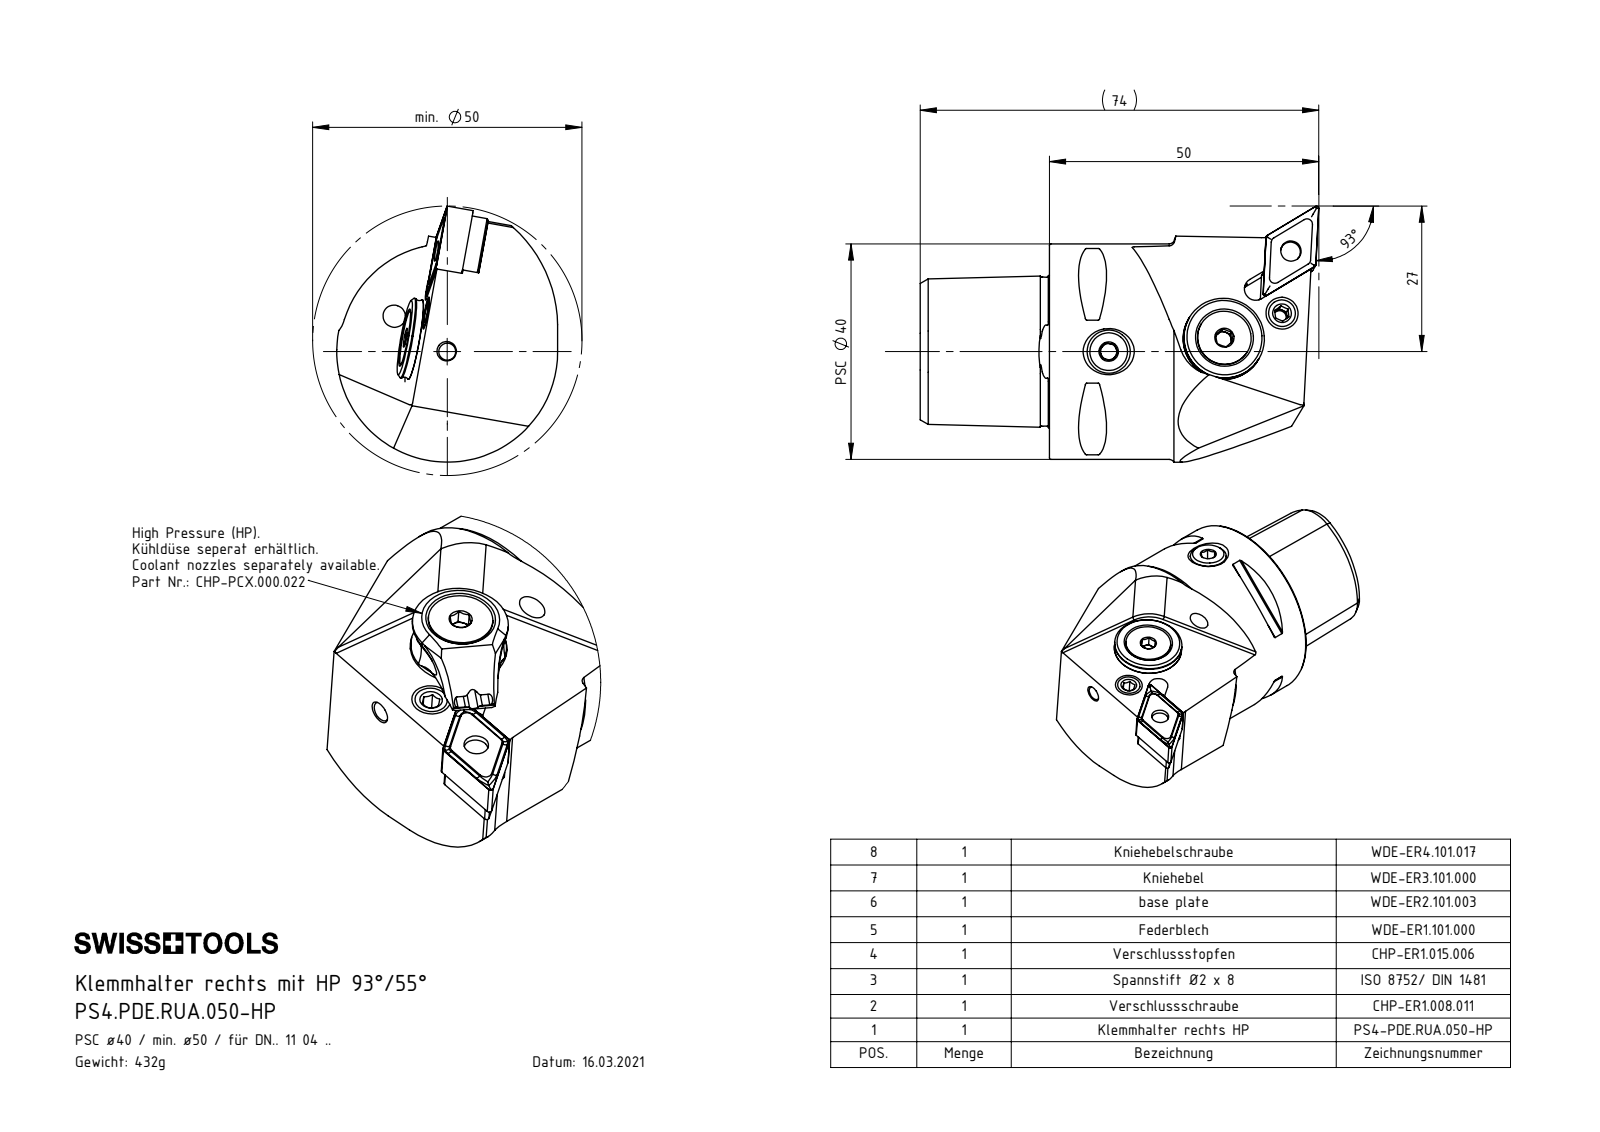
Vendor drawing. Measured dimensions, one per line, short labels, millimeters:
name: PS4-PDE.RUA.050-HP_A; DIN 7991 - M5x18; WDE-ER3.101.000_A; WDE-ER4.101.017_A (+8 more)
written by: SolidWorks 2022 (CONFIG_CONTROL_DESIGN)
unit: mm
bodies: 12 solids, 578 faces (160 planar, 148 cylindrical, 270 other)
size: 74 × 47.49 × 41
volume: 55 931 mm³; area: 18 264 mm²
holes: 3× ⌀4.2, 2× ⌀5, 1× ⌀1.2, 1× ⌀2, 1× ⌀2.5, 1× ⌀3, 1× ⌀3.15, 1× ⌀3.81, 1× ⌀4, 1× ⌀4.6, 1× ⌀4.8, 1× ⌀5.3
bosses: 1× ⌀40, 1× ⌀14.85, 1× ⌀13.4, 1× ⌀10, 1× ⌀8, 1× ⌀6, 1× ⌀5.9, 1× ⌀5.5
rounds: 9× R0.3, 7× R1, 4× R0.4, 4× R0.5, 4× R0.8, 4× R2.1, 3× R6, 2× R1.1
face distances: 24, 4.51, 4.63, 9, 15.52, 1.5, 3.01, 8.7, 1.62, 0.53
hole spacings: 11.29, 12.11, 4.5, 4.52, 11.79, 1, 17.85, 17.86
